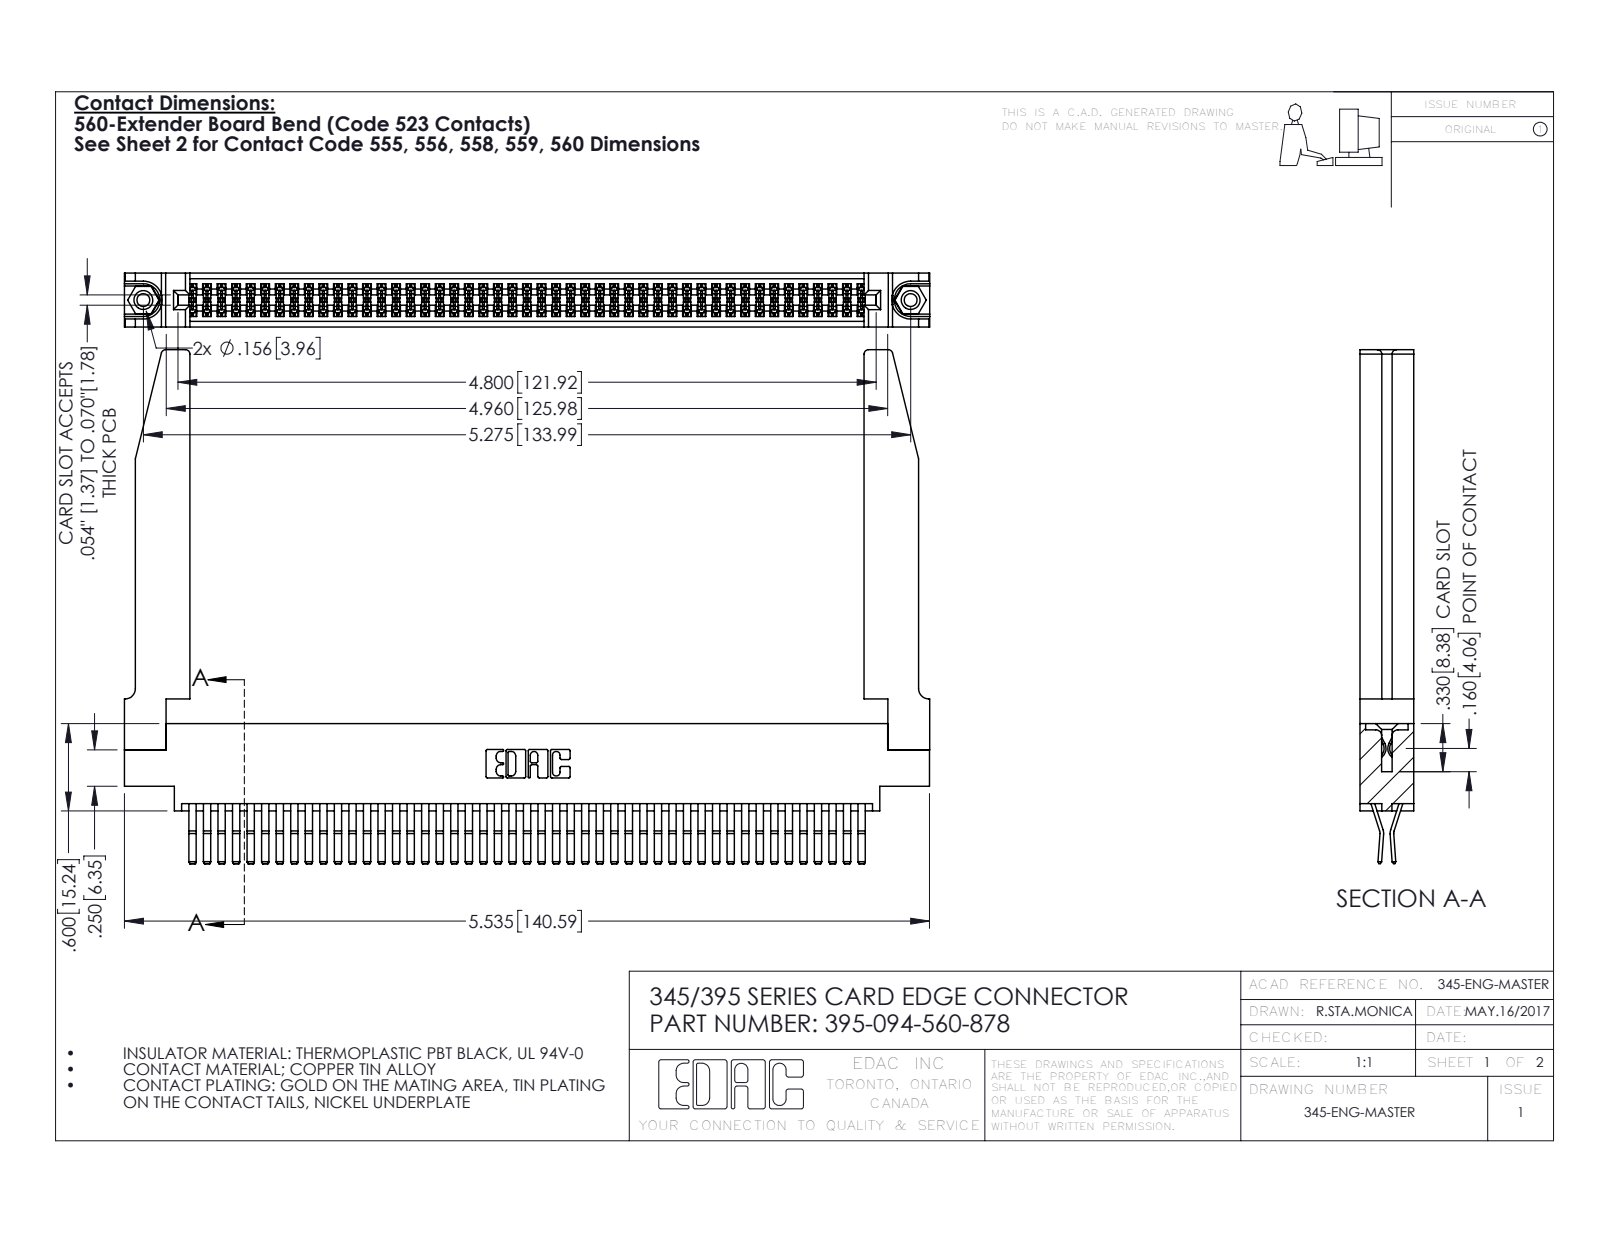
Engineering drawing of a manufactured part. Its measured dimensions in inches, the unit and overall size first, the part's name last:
Units: inches
Overall size (bounding box): 5.536 × 3.532 × 0.37
Round holes (diameter × count): ⌀0.089 ×2, ⌀0.125 ×2, ⌀0.156 ×2, ⌀0.064 ×1
Round bosses / shafts (diameter × count): ⌀0.155 ×2
Partial cylindrical surfaces — rounded edges, fillets, slot ends (radius × count): R0.006 ×141, R0.01 ×22, R0.03 ×8, R0.007 ×6, R0.031 ×6, R0.026 ×3, R0.01 ×2, R0.014 ×2
Main face-to-face distances: 0.37, 0.072, 0.298, 0.025, 0.098, 0.272, 0.2, 0.225, 0.175, 0.148
Hole centre spacings: 0.27, 5.039, 5.275
Volume: 1.341 in³ · Surface area: 45.98 in²
Bodies: 99 solids, 5252 faces (3328 planar, 1872 cylindrical, 52 other)
Part name (STEP PRODUCT): 345-292-001_560 Tail; 345-220-078_345-220-078; 395-094-560-878; 345-250-001_345-250-001-102 (+1 more)
STEP written by: SolidWorks 2016 (CONFIG_CONTROL_DESIGN)
